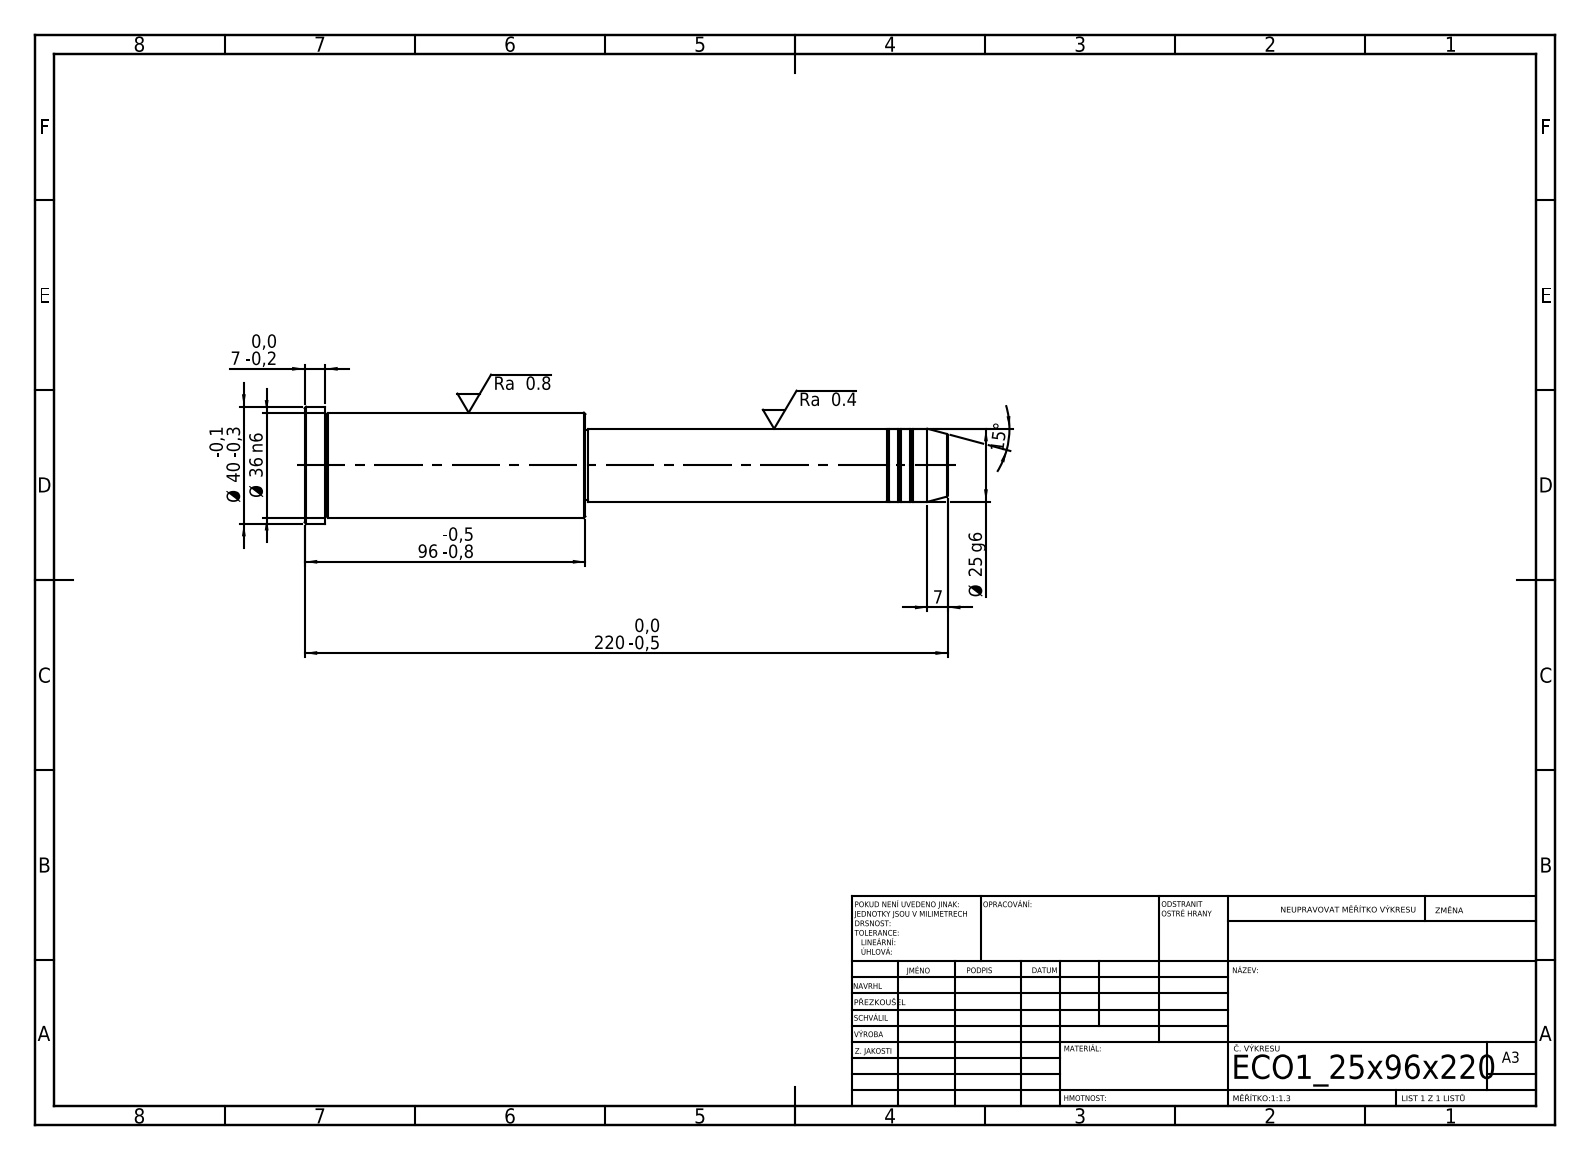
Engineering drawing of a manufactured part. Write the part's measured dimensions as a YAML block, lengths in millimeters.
step_written_by: "SolidWorks 2019 (CONFIG_CONTROL_DESIGN)"
units: millimeters
bodies: {solids: 1, faces: 43, planar: 5, cylindrical: 14, other: 24}
overall_size: [220, 40, 40]
volume: 159561
surface_area: 23220
round_bosses_or_shafts:
  - {diameter: 40, count: 1}
  - {diameter: 36, count: 1}
  - {diameter: 25, count: 1}
  - {diameter: 24, count: 1}
face_to_face_distances: [96, 124, 220, 213, 89, 7, 123, 1, 90, 97]
